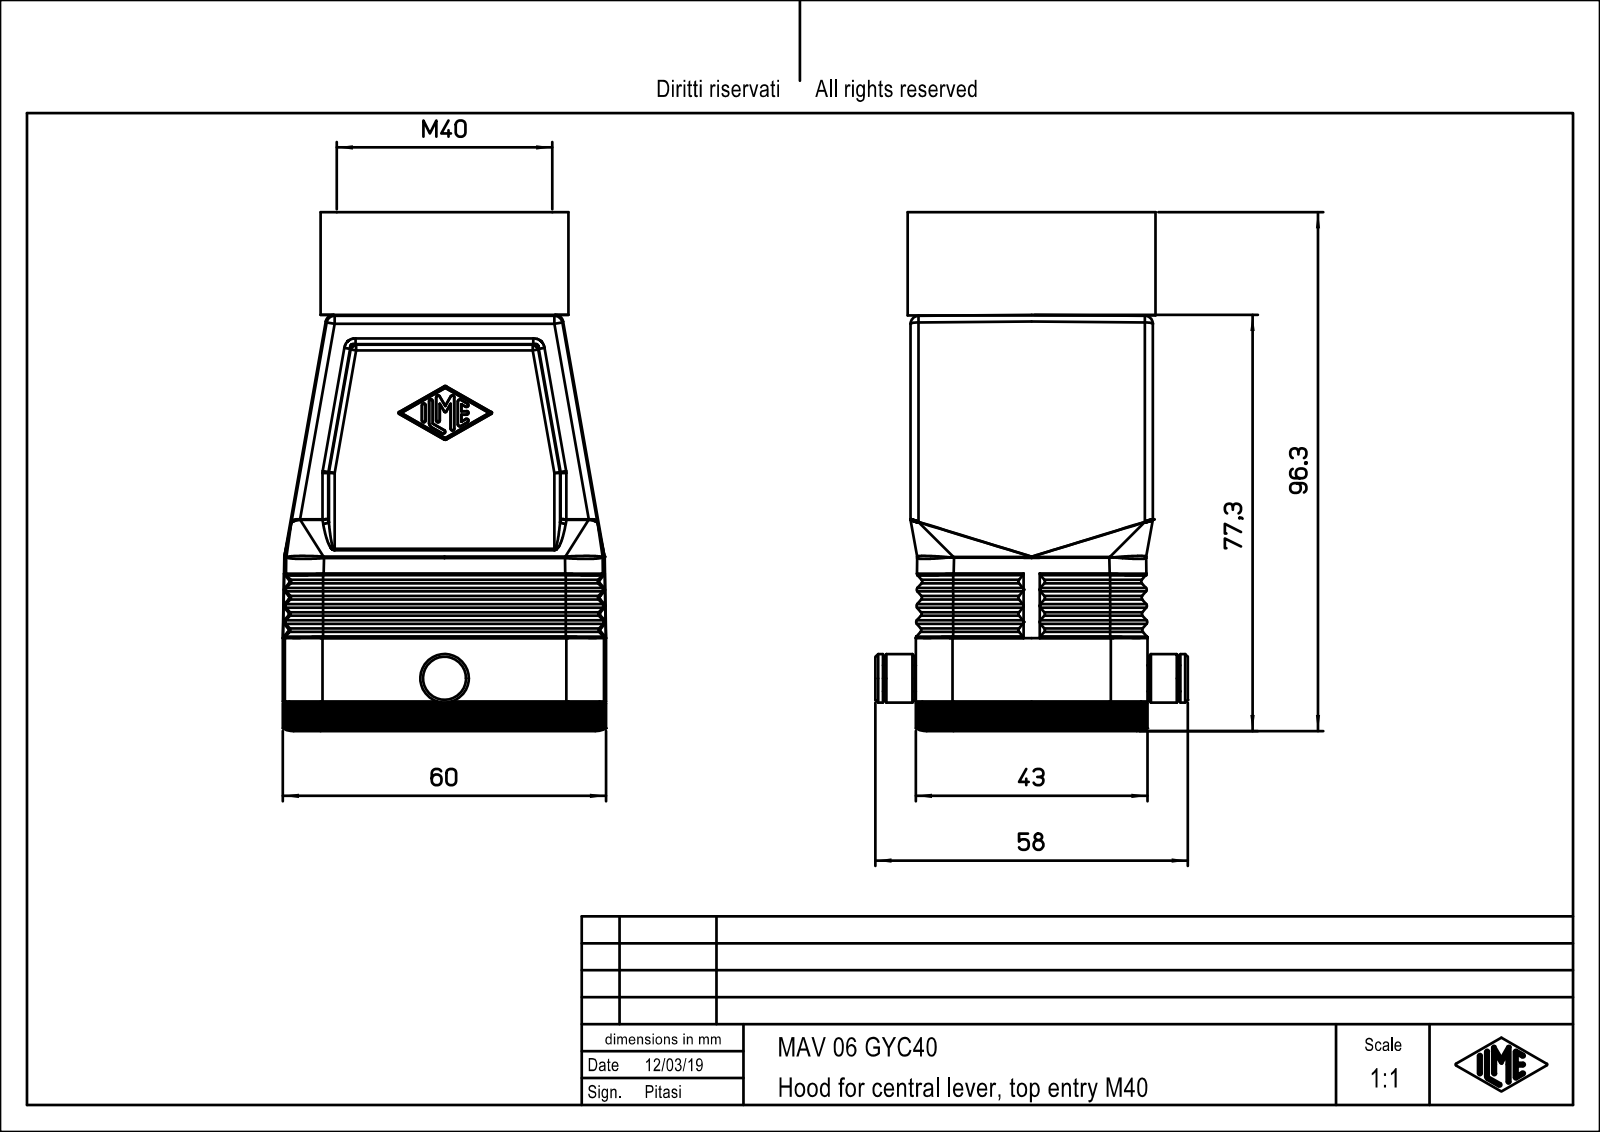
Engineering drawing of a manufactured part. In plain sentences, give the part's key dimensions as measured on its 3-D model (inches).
The part is named "MAV_06_GYC40". Its 3-D file was written by "PTC Creo Elements/Direct Modeling 19.0E 27-Jun-2016 (C) Parametric Technology GmbH (AUTOMOTIVE_DESIGN)". It is 1 solid with 536 faces: 176 planar, 180 cylindrical and 180 other. Overall it measures 3.789 by 2.362 by 2.283 inches. Its volume is 4.344 cubic inches and its surface area 58.8 square inches. Round holes: 4 of diameter 0.118, 1 of diameter 1.339. Round bosses or shafts: 1 of diameter 1.811, 1 of diameter 1.575, 1 of diameter 0.354, 1 of diameter 0.189. Partial cylindrical surfaces (rounded edges, fillets, slot ends): 54 of radius 0.02, 44 of radius 0.059, 12 of radius 0.118, 12 of radius 0.276, 4 of radius 0.157, 4 of radius 0.165, 4 of radius 0.228. The main face-to-face distances are 1.693, 0.276, 0.157, 0.079, 0.297, 0.039, 1.732, 1.535, 0.453, 2.362. The hole center spacings are 1.016, 1.063, 1.732, 2.032.
